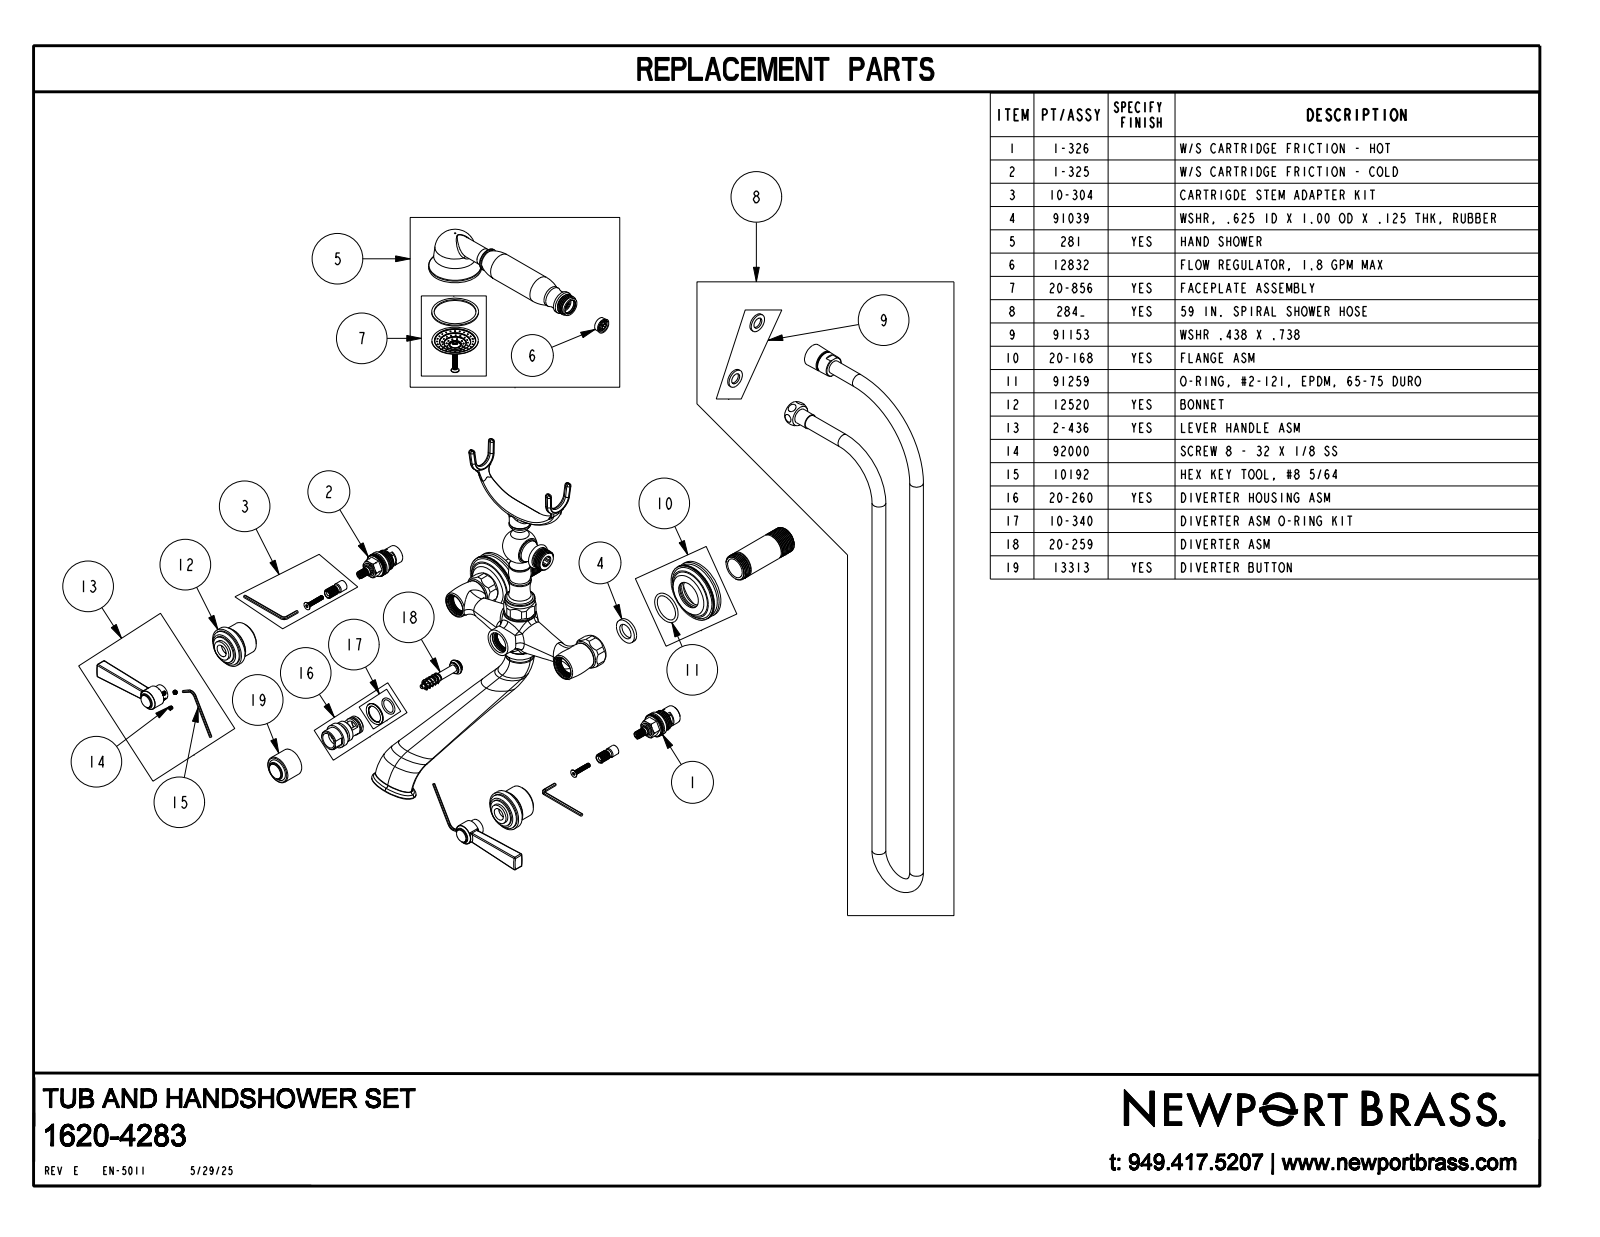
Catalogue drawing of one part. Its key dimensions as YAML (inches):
part_name: "1620-4283"
step_written_by: "CREO PARAMETRIC BY PTC INC, 2018400 (CONFIG_CONTROL_DESIGN)"
units: inches
bodies: {solids: 1, faces: 1626, planar: 650, cylindrical: 533, other: 443}
overall_size: [23.86, 14.123, 9.328]
volume: 49.91
surface_area: 284.4
round_holes:
  - {diameter: 0.046, count: 52}
  - {diameter: 1.095, count: 2}
  - {diameter: 1.26, count: 2}
  - {diameter: 1.9, count: 2}
  - {diameter: 2.24, count: 2}
round_bosses_or_shafts:
  - {diameter: 0.82, count: 4}
  - {diameter: 0.54, count: 4}
  - {diameter: 1.1, count: 3}
  - {diameter: 2.35, count: 2}
  - {diameter: 2.25, count: 2}
  - {diameter: 2, count: 2}
  - {diameter: 1.6, count: 2}
  - {diameter: 1.45, count: 2}
partial_cylinders:
  - {radius: 0.085, count: 32}
  - {radius: 0.04, count: 4}
  - {radius: 0.055, count: 4}
  - {radius: 0.637, count: 3}
  - {radius: 0.595, count: 2}
  - {radius: 0.405, count: 1}
  - {radius: 0.406, count: 1}
  - {radius: 0.45, count: 1}
face_to_face_distances: [0.275, 0.2, 0.1, 0.35, 1.188, 3, 3.096, 0.265, 0.54, 0.19]
hole_center_spacings: [0.187, 0.367, 0.535, 0.813, 1.021, 0.184, 0.601, 0.685]
